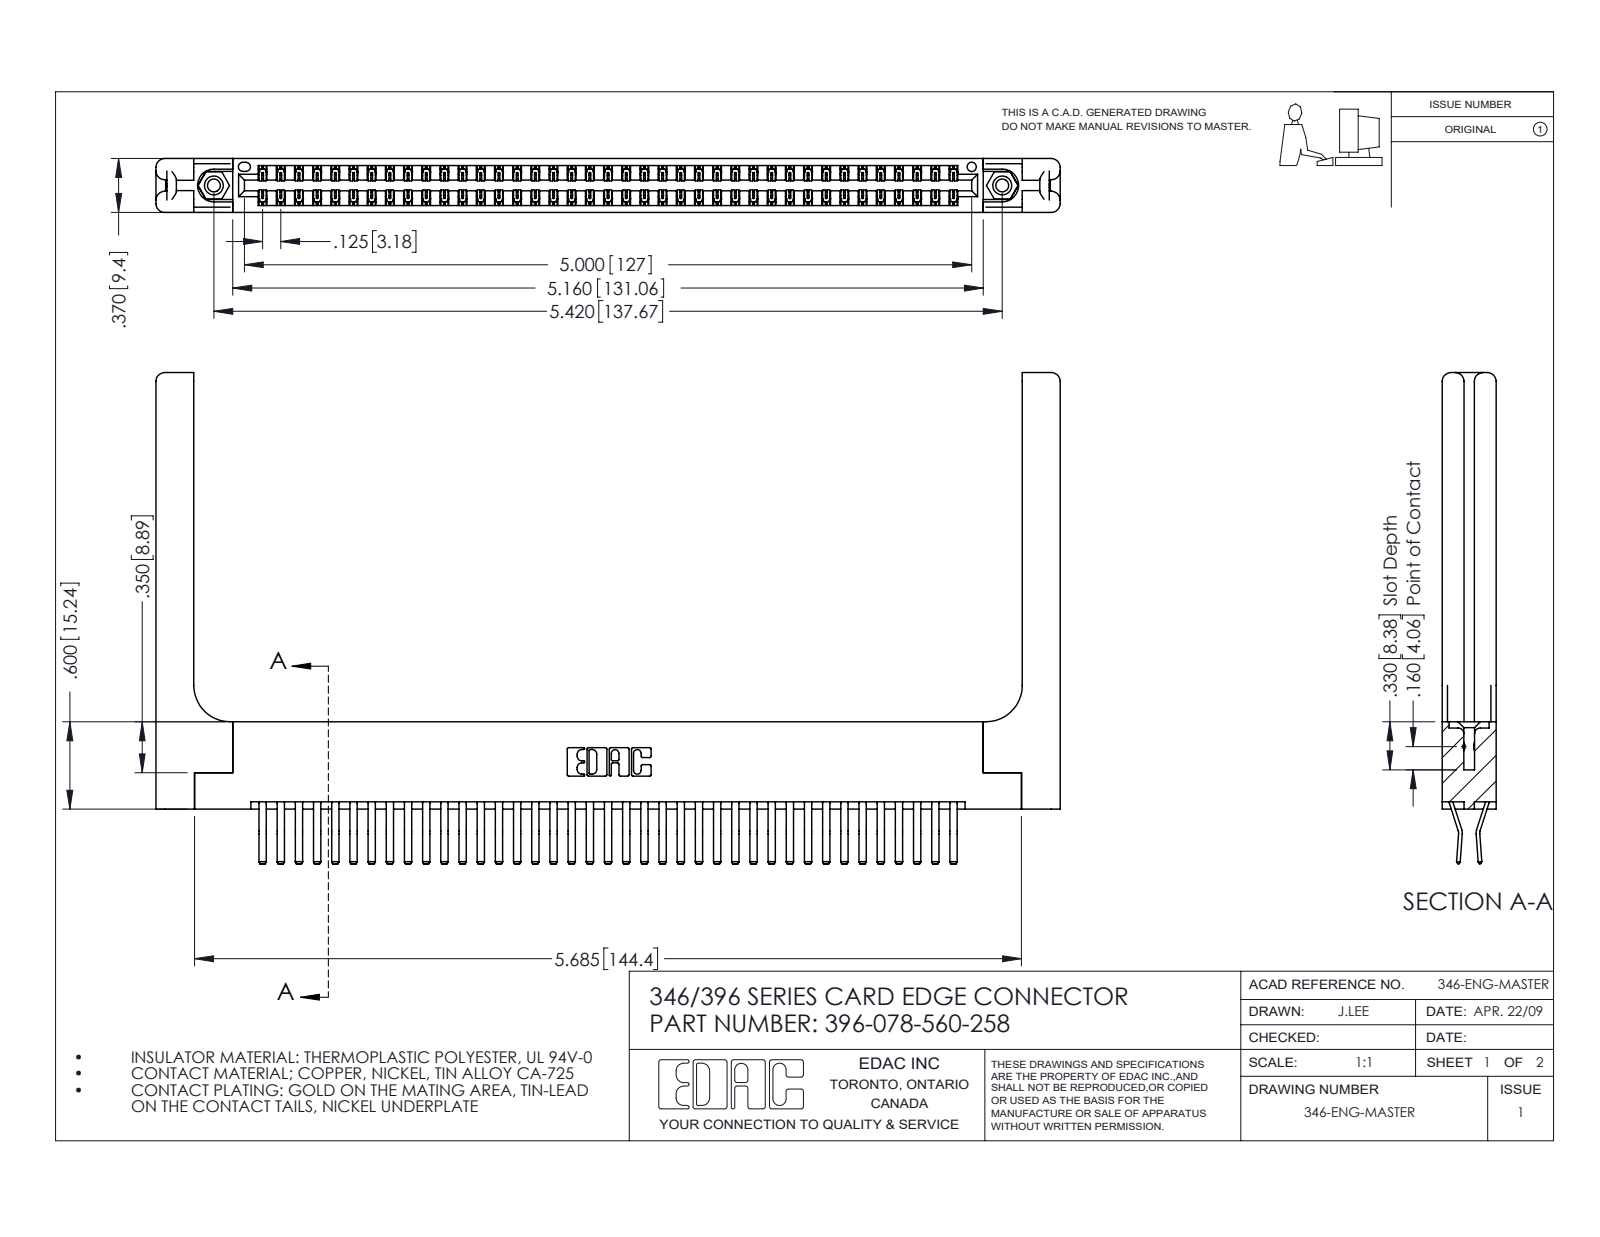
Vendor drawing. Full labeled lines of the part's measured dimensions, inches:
Part name (STEP PRODUCT): 396-078-560-258; 346 Part_Flush Mounting Lugs - 0.156 Dia-TH; 345-250-001_345-250-001-102; 346-220-058_345-220-058 (+1 more)
STEP written by: SolidWorks 2016 (CONFIG_CONTROL_DESIGN)
Units: inches
Bodies: 83 solids, 4590 faces (2954 planar, 1576 cylindrical, 60 other)
Overall size (bounding box): 6.216 × 3.375 × 0.37
Volume: 1.427 in³ · Surface area: 43.59 in²
Round holes (diameter × count): ⌀0.089 ×2, ⌀0.125 ×2, ⌀0.156 ×2, ⌀0.064 ×1
Round bosses / shafts (diameter × count): ⌀0.155 ×2
Partial cylindrical surfaces — rounded edges, fillets, slot ends (radius × count): R0.006 ×117, R0.01 ×22, R0.06 ×16, R0.007 ×6, R0.031 ×6, R0.026 ×3, R0.01 ×2, R0.014 ×2
Main face-to-face distances: 0.37, 0.048, 0.322, 0.072, 0.025, 0.148, 0.15, 0.25, 0.298, 0.275
Hole centre spacings: 0.246, 5.211, 5.42
